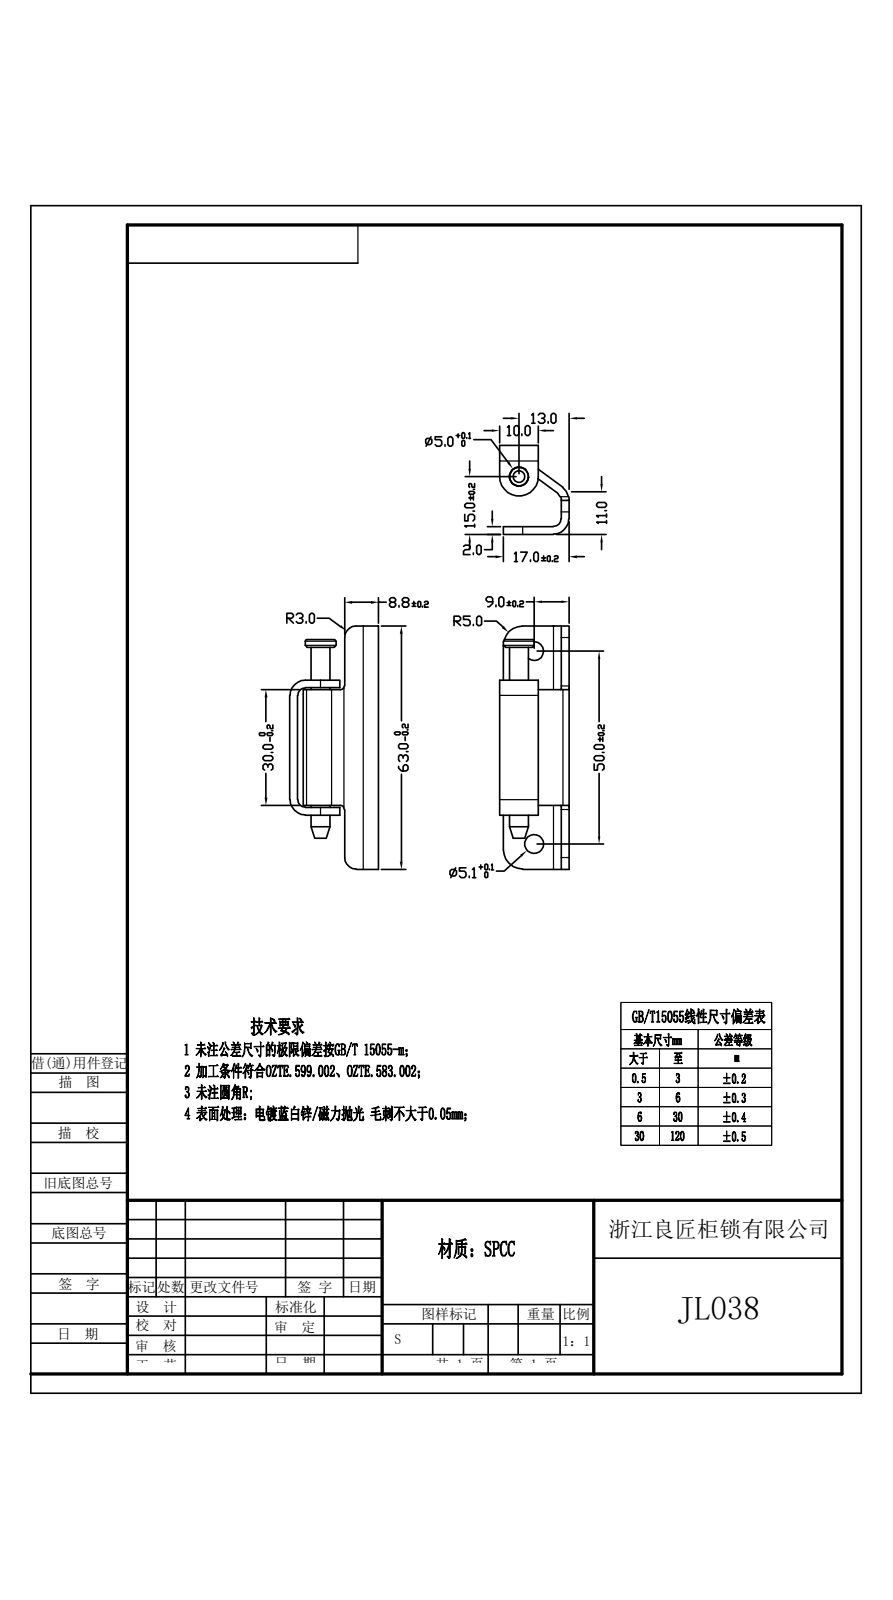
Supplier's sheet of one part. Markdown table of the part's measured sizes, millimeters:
| quantity | value |
| --- | --- |
| STEP written by | Rhino 8.5 (CONFIG_CONTROL_DESIGN) |
| units | millimeters |
| bodies | 3 solids, 61 faces (25 planar, 30 cylindrical, 6 other) |
| overall size | 63 × 23 × 18.25 |
| volume | 6 643 mm³ |
| surface area | 7 348 mm² |
| round holes (diameter × count) | 5.1 × 3, 5 × 1 |
| round bosses / shafts (diameter × count) | 9 × 1, 8 × 1, 4.9 × 1 |
| partial cylindrical surfaces (radius × count) | 2 × 4, 4 × 4, 5 × 3, 3 × 2 |
| main face-to-face distances | 2, 20.99, 1.98, 22.99, 18.99, 0.5, 30.5, 2.5, 32.5, 33 |
| hole center spacings | 0.51, 50 |
